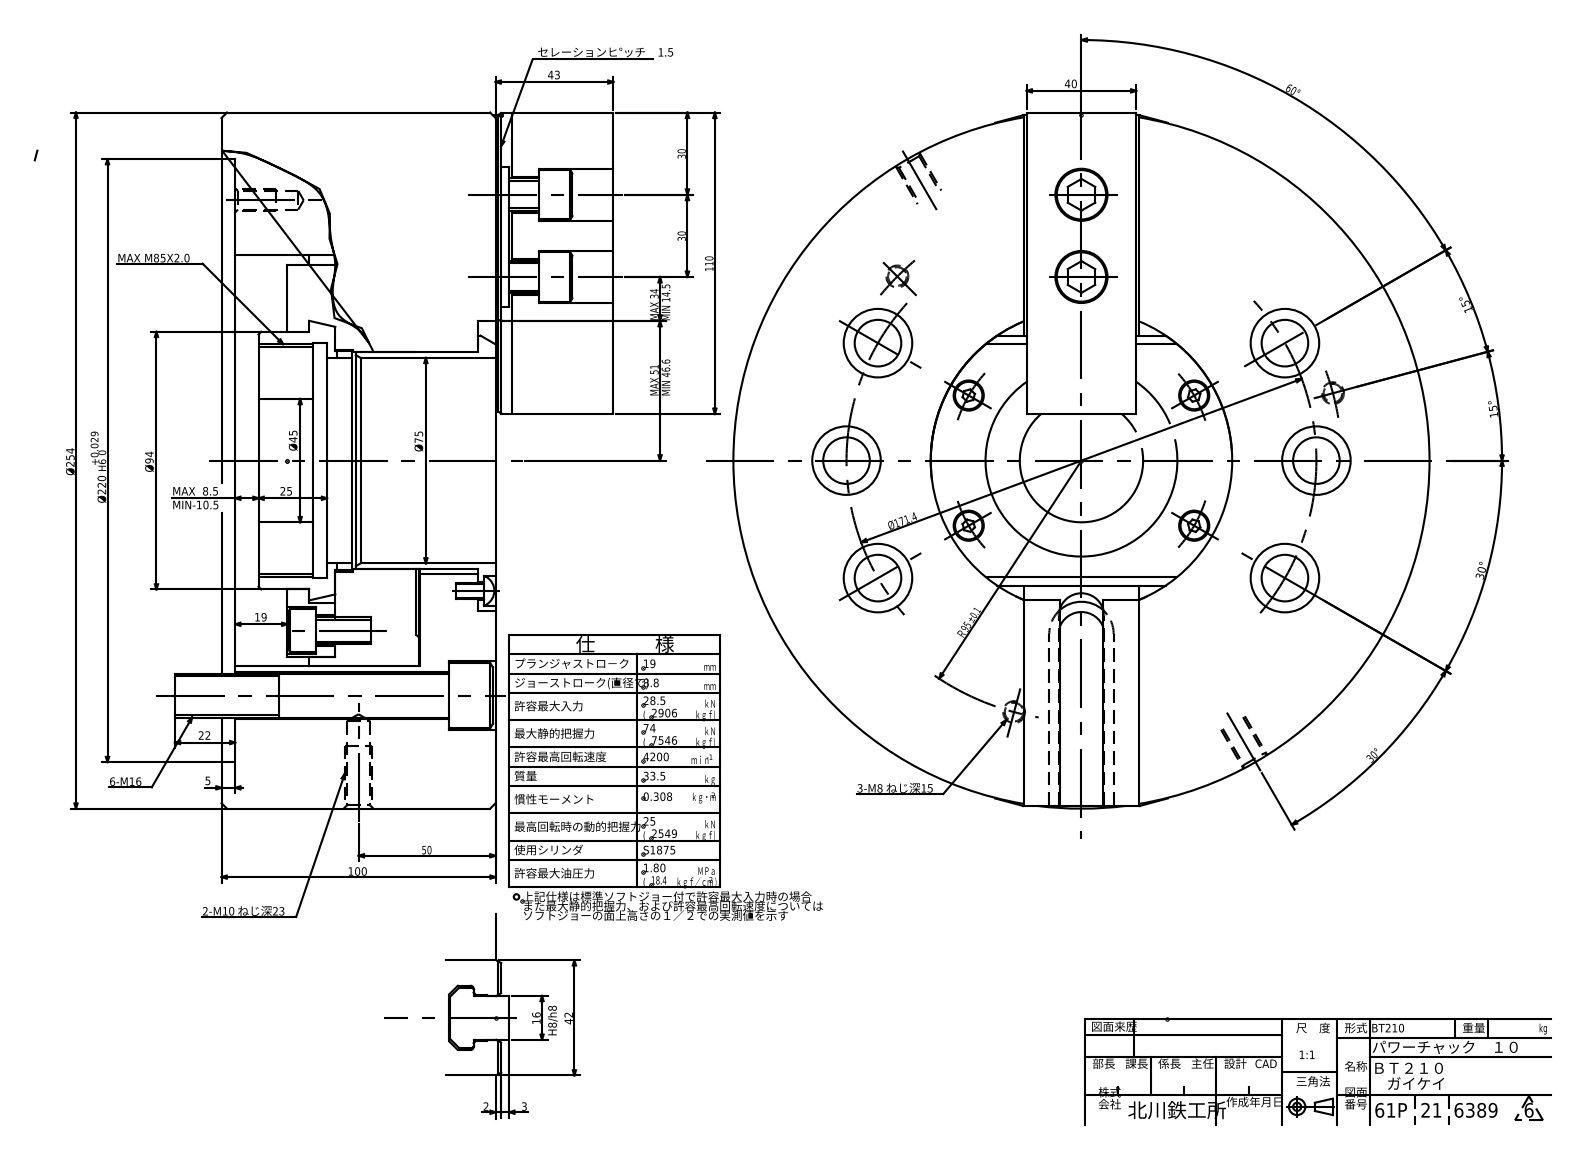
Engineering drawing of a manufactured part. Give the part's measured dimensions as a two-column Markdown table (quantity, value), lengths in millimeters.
| quantity | value |
| --- | --- |
| part name | BT210_mid stroke |
| STEP written by | ST-DEVELOPER v16.7 (AUTOMOTIVE_DESIGN) |
| units | millimeters |
| bodies | 1 solid, 3076 faces (2227 planar, 648 cylindrical, 201 other) |
| overall size | 254 × 254 × 160.2 |
| volume | 4 457 000 mm³ |
| surface area | 468 830 mm² |
| round holes (diameter × count) | 17 × 12, 5.2 × 10, 11 × 10, 25 × 6, 6.6 × 4, 10.3 × 4, 13 × 4, 19 × 4, 6.8 × 3, 8.5 × 2, 45 × 1, 75 × 1 |
| round bosses / shafts (diameter × count) | 24 × 6, 16 × 6, 15.68 × 6, 9.73 × 6, 18 × 4, 11.7 × 4, 10.5 × 4, 5.79 × 4 |
| partial cylindrical surfaces (radius × count) | 0.15 × 102, 0.4 × 14, 5 × 6, 6.75 × 4, 9.5 × 4, 0.8 × 2, 1.2 × 2, 3.1 × 2 |
| main face-to-face distances | 95, 9.5, 58, 5, 10.5, 20, 100, 67.5, 4, 24 |
| hole center spacings | 44.57, 62, 85.72, 142.82, 47.5, 147.72, 14.49, 23.73 |
